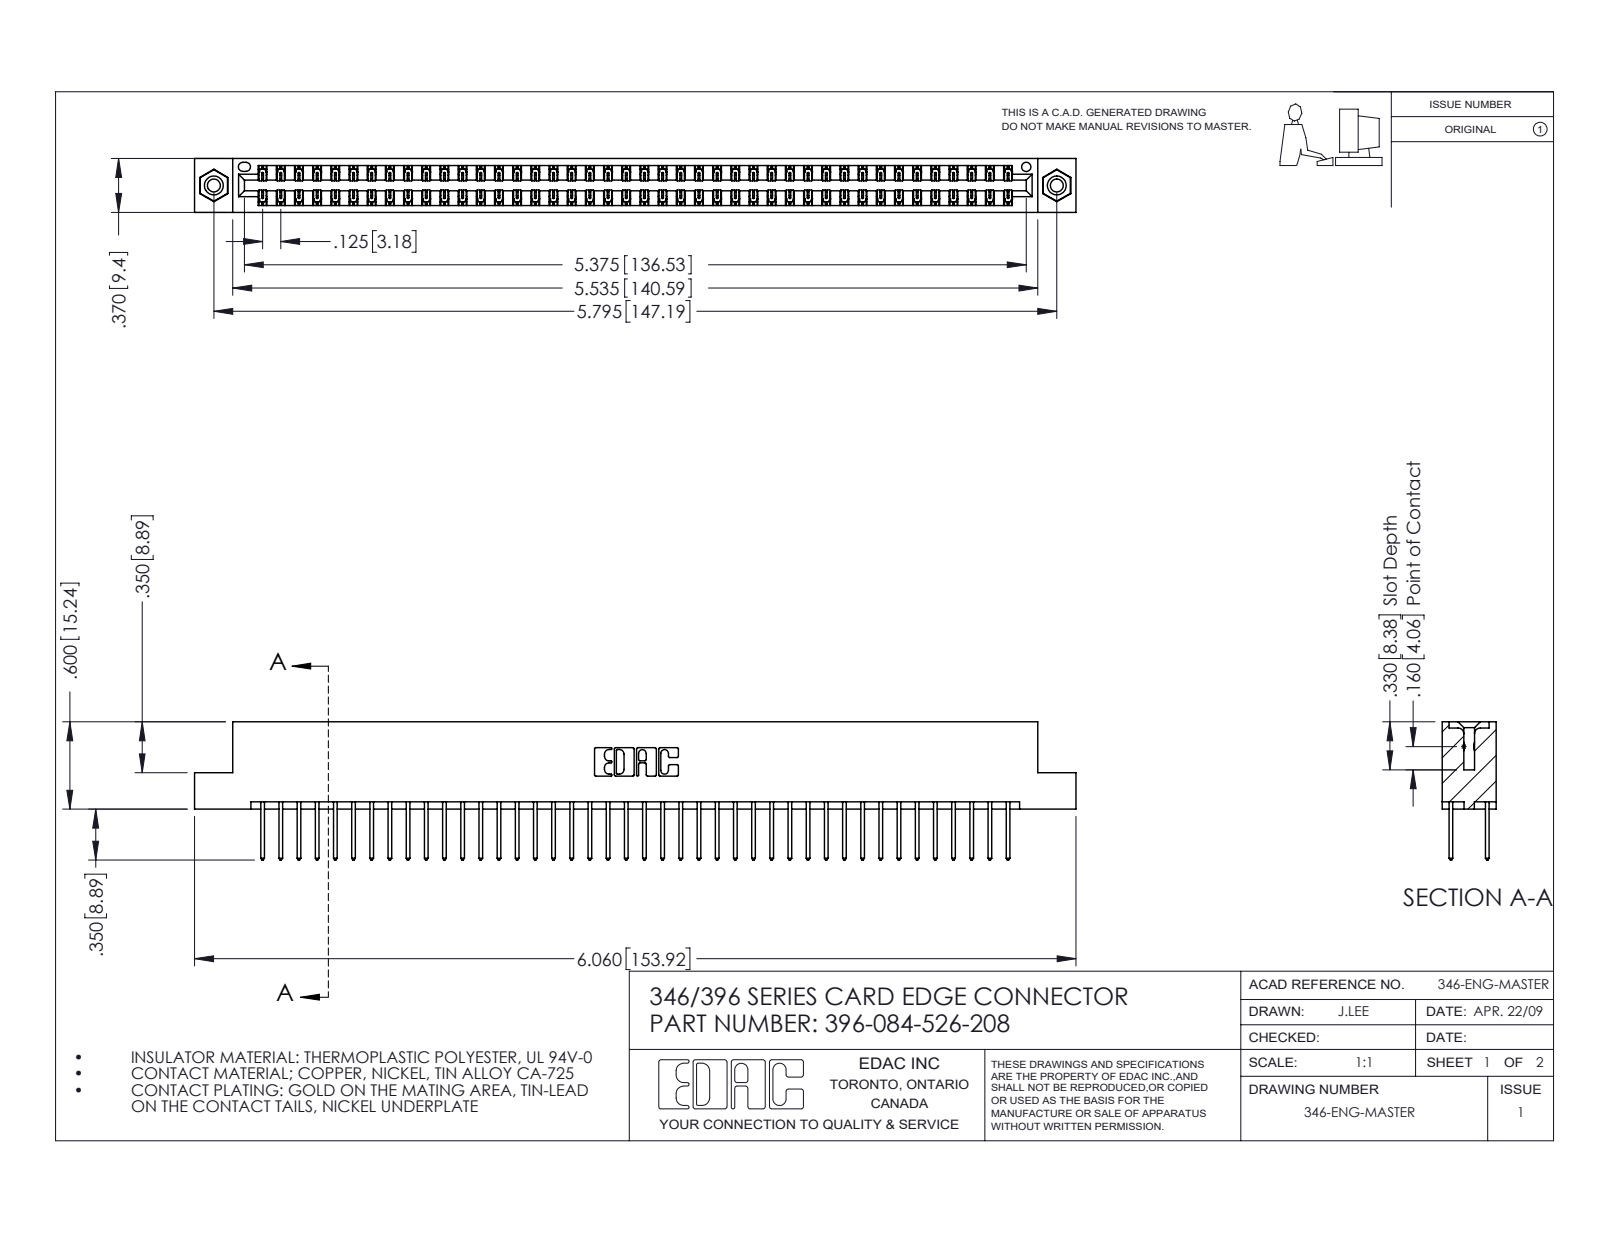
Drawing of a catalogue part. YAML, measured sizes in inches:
part_name: "345-292-001_345-293-126; 396-084-526-208; 345-250-001_345-250-003-102; 346 Part_Flush Mounting Lugs - 0.156 Dia-TI"
step_written_by: "SolidWorks 2016 (CONFIG_CONTROL_DESIGN)"
units: inches
bodies: {solids: 87, faces: 4550, planar: 3048, cylindrical: 1486, other: 16}
overall_size: [6.06, 0.95, 0.37]
volume: 0.924
surface_area: 33.25
round_holes:
  - {diameter: 0.089, count: 2}
  - {diameter: 0.125, count: 2}
  - {diameter: 0.156, count: 2}
  - {diameter: 0.064, count: 1}
round_bosses_or_shafts:
  - {diameter: 0.155, count: 2}
partial_cylinders:
  - {radius: 0.006, count: 126}
  - {radius: 0.01, count: 84}
  - {radius: 0.01, count: 22}
  - {radius: 0.007, count: 6}
  - {radius: 0.031, count: 6}
  - {radius: 0.026, count: 3}
  - {radius: 0.014, count: 2}
  - {radius: 0.022, count: 2}
face_to_face_distances: [0.048, 0.322, 0.25, 0.37, 0.072, 0.298, 0.025, 0.275, 0.148, 0.222]
hole_center_spacings: [0.246, 5.586, 5.795]
